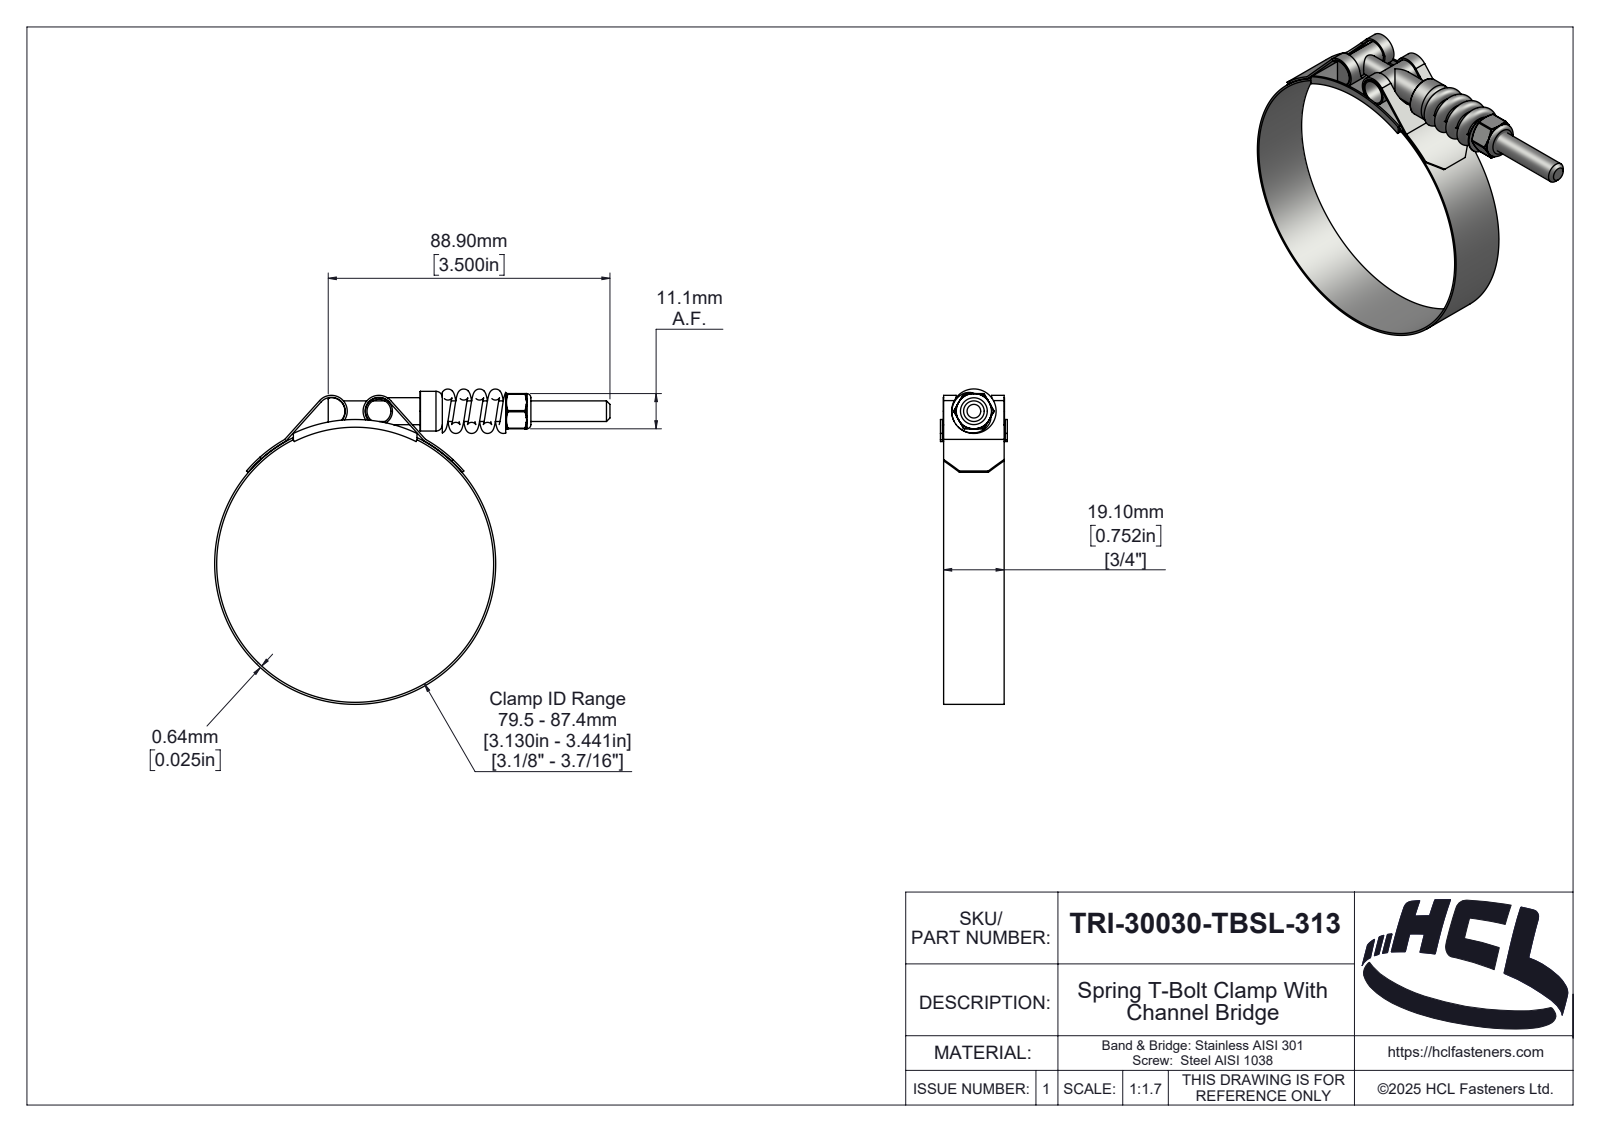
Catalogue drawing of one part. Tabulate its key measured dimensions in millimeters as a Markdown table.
| quantity | value |
| --- | --- |
| part name | TRI-30030-TBSL-313 |
| STEP written by | SolidWorks 2025 (AUTOMOTIVE_DESIGN) |
| units | millimeters |
| bodies | 7 solids, 332 faces (48 planar, 122 cylindrical, 162 other) |
| overall size | 125.74 × 99.48 × 21.1 |
| volume | 11 151 mm³ |
| surface area | 21 953 mm² |
| round holes (diameter × count) | 5.4 × 1, 6.35 × 1, 6.5 × 1, 7.52 × 1, 87.4 × 1 |
| round bosses / shafts (diameter × count) | 8.52 × 2, 88.68 × 1, 12.52 × 1 |
| partial cylindrical surfaces (radius × count) | 0.39 × 6, 0.5 × 2, 4.36 × 2, 5 × 2, 0.59 × 1, 2.42 × 1, 3.03 × 1, 3.19 × 1 |
| main face-to-face distances | 0.64, 19.1, 1, 20.1, 20.46, 0.36, 19.46, 56, 11.12, 0.9 |
| hole center spacings | 48.7 |
